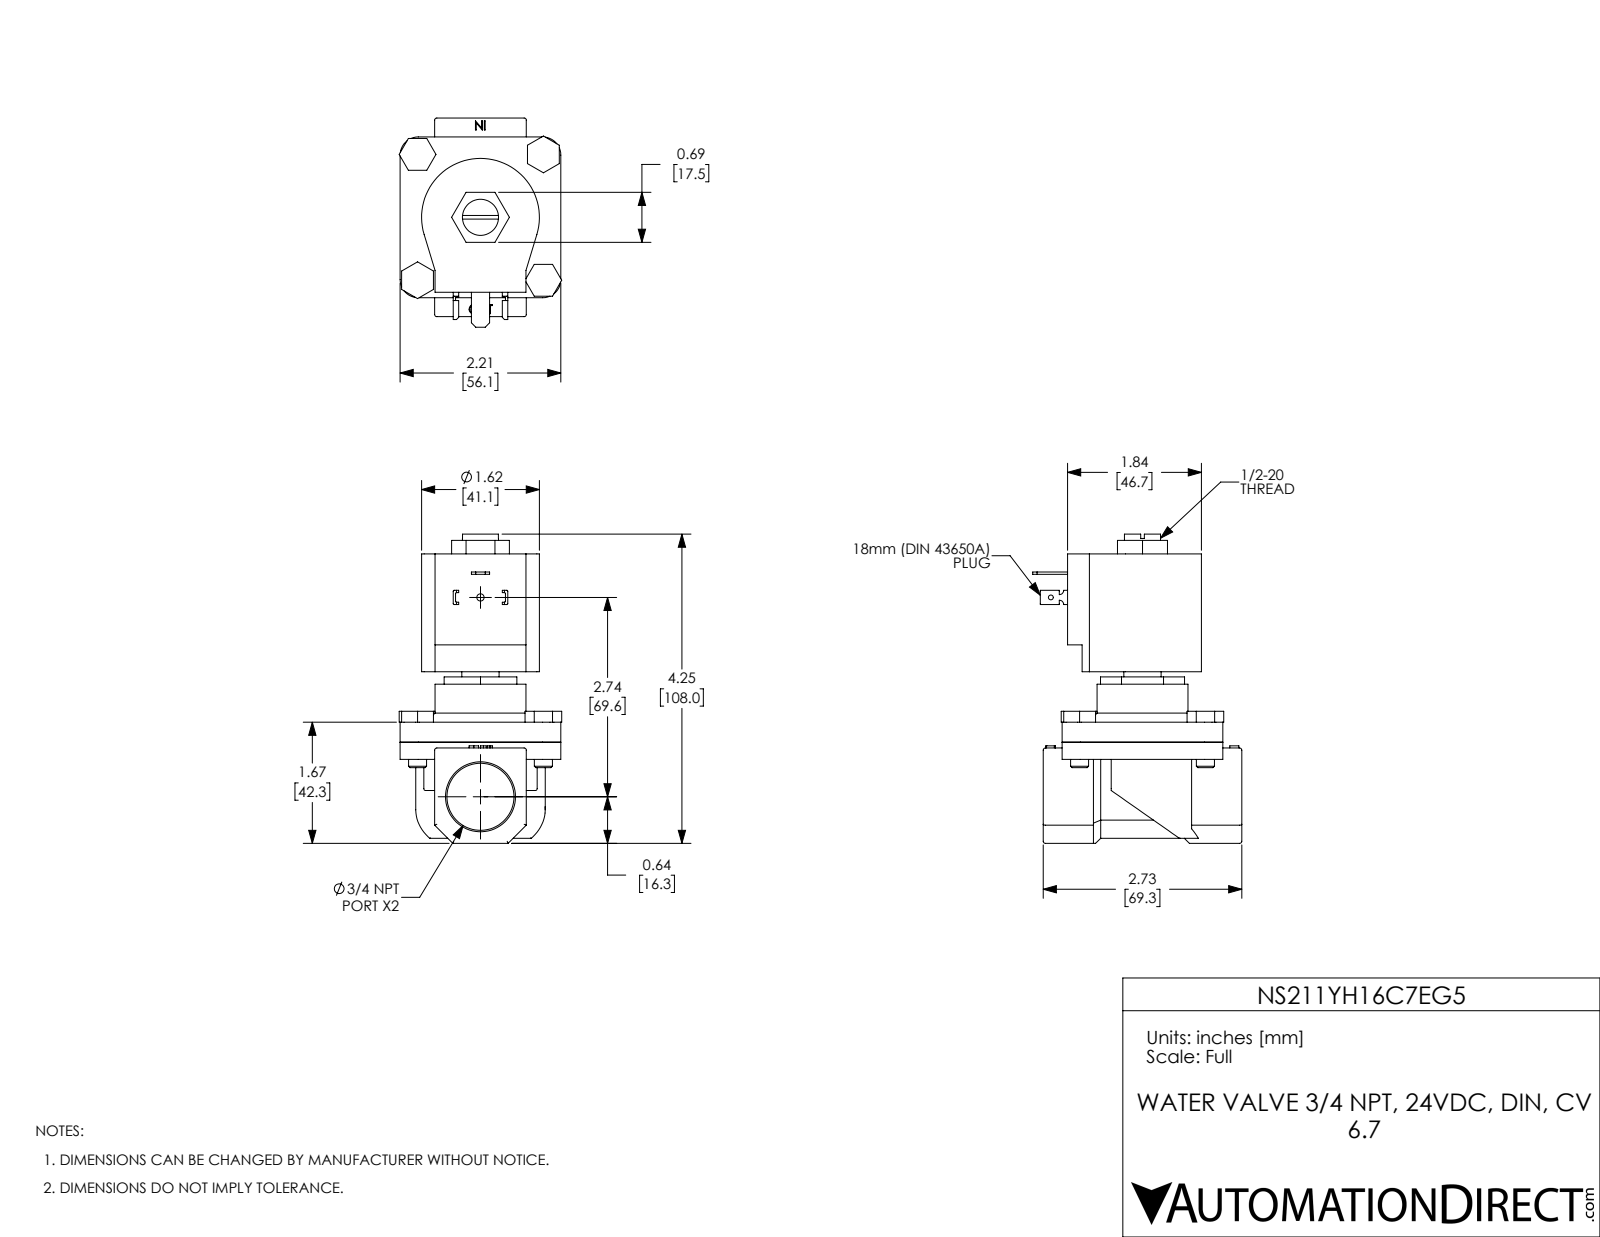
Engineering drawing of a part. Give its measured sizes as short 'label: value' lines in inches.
name: NS211YH16C7EG5
written by: SolidWorks 2024 (CONFIG_CONTROL_DESIGN)
unit: in
bodies: 11 solids, 332 faces (198 planar, 99 cylindrical, 35 other)
size: 4.25 × 2.875 × 2.235
volume: 10.48 in³; area: 66.73 in²
holes: 4× ⌀0.25, 1× ⌀0.067, 1× ⌀0.1, 1× ⌀0.496, 1× ⌀0.512, 1× ⌀0.922, 1× ⌀1.155
bosses: 4× ⌀0.248, 1× ⌀1.25
rounds: 15× R0.03, 8× R0.015, 4× R0.25, 2× R0.06, 1× R0.81, 1× R0.89
face distances: 0.275, 2.588, 2.313, 0.475, 1.735, 2.21, 0.236, 0.511, 2.824, 0.26
hole spacings: 1.223, 1.73, 2.446, 2.74
